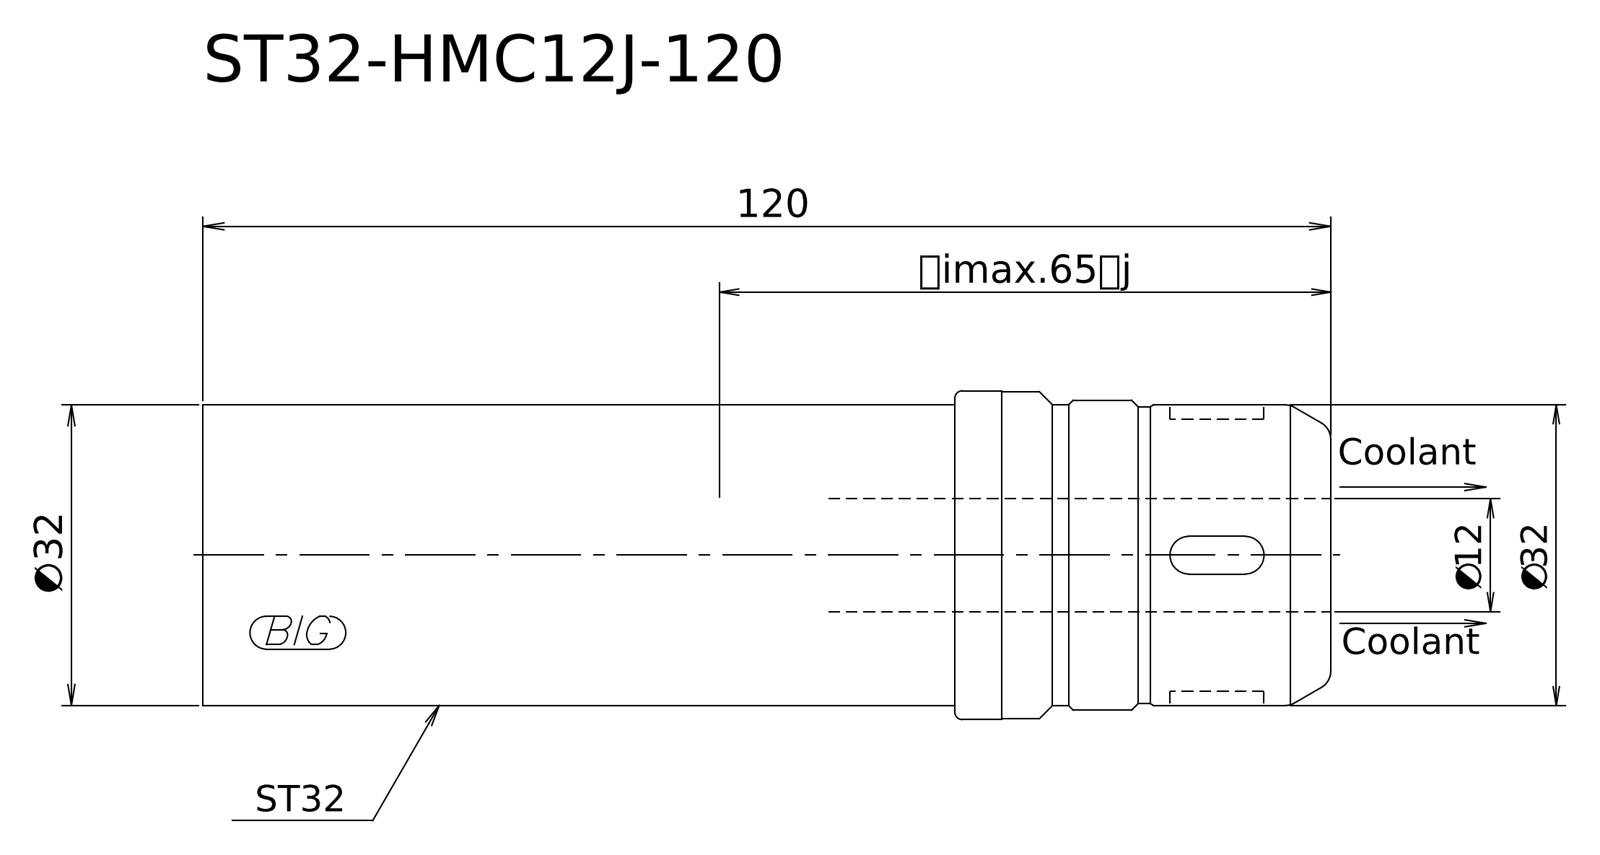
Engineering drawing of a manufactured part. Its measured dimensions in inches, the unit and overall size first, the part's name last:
Units: inches
Overall size (bounding box): 4.724 × 1.378 × 1.378
Round bosses / shafts (diameter × count): ⌀1.378 ×1, ⌀1.299 ×1, ⌀1.26 ×1, ⌀1.244 ×1
Main face-to-face distances: 4.724, 1.575, 3.15
Volume: 5.97 in³ · Surface area: 21.48 in²
Bodies: 1 solid, 14 faces (3 planar, 6 cylindrical, 5 other)
STEP written by: Kubotek KeyCreator 2011 V10.0.2 (22737) (automotive_design)
